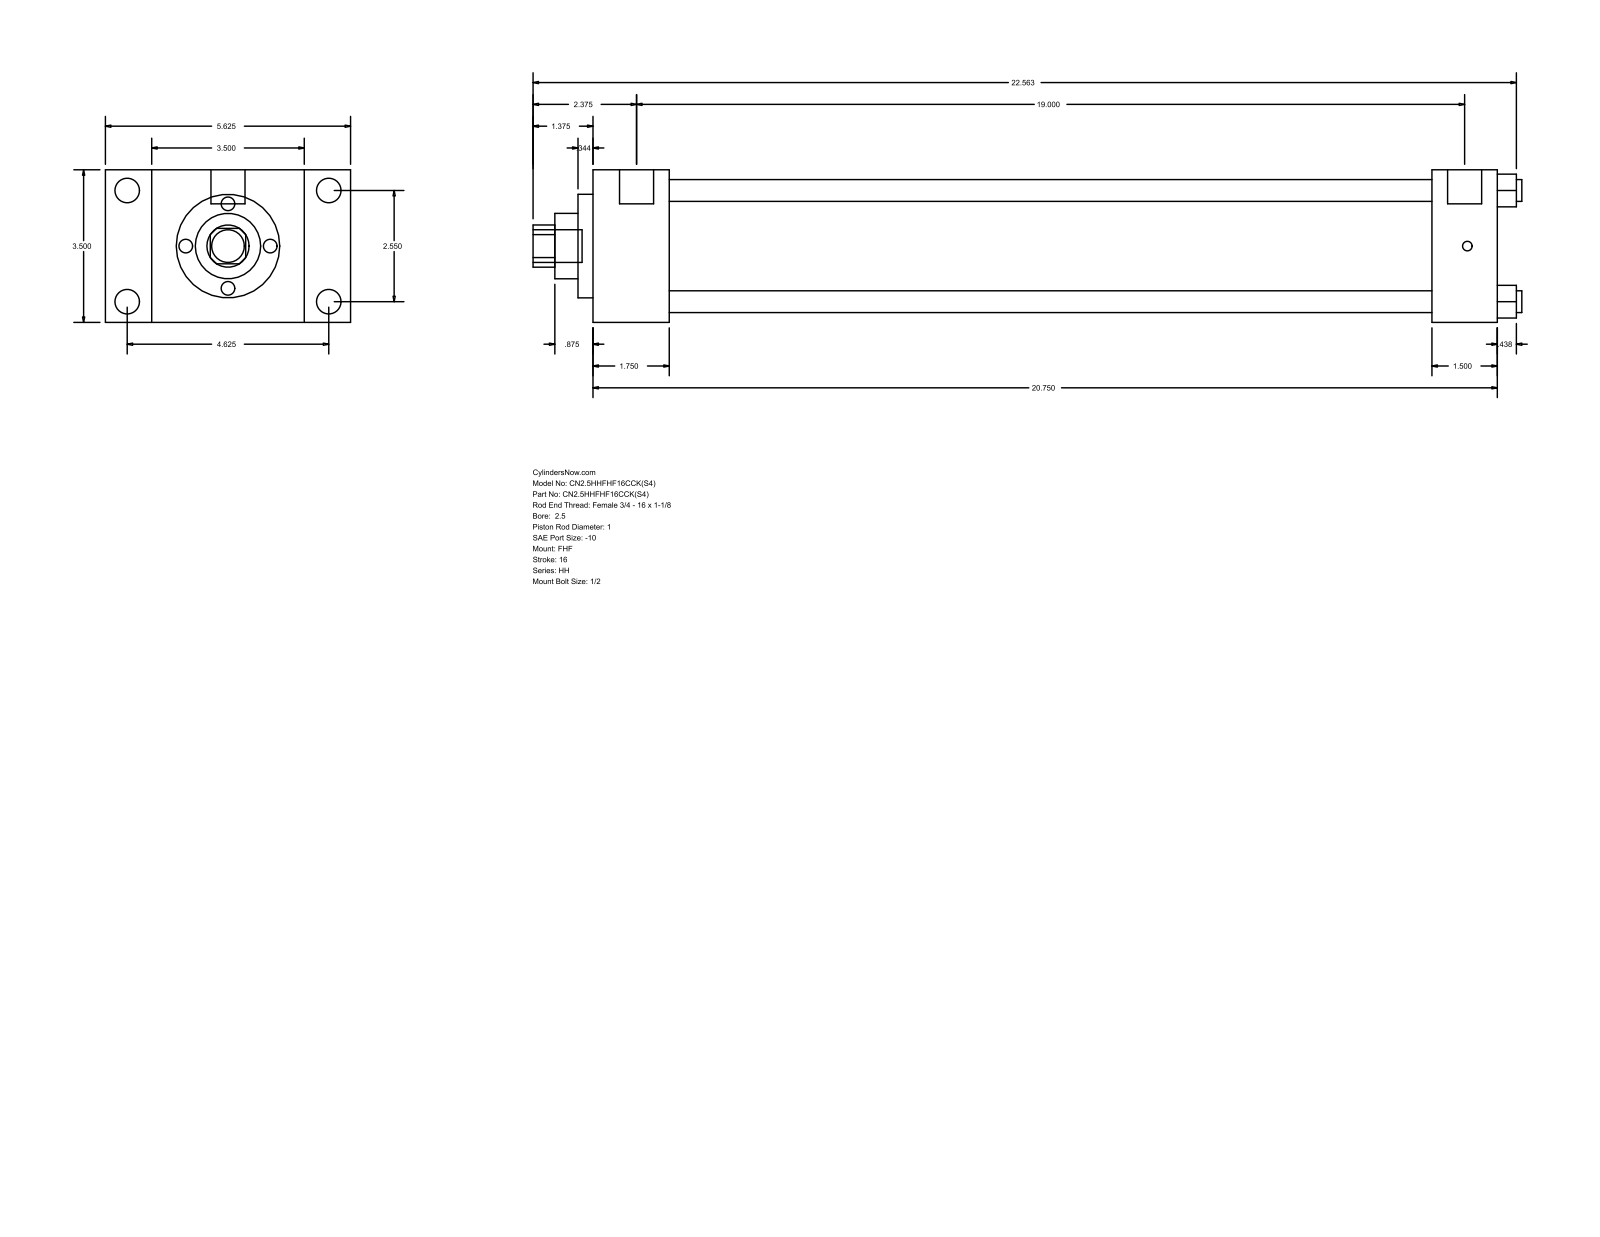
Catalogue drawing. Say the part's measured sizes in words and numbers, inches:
The part is named "HH_FHF__0250_1". Its 3-D file was written by "GSSL Pune (CONFIG_CONTROL_DESIGN)". It is 0 solids with 90 faces: 61 planar, 29 cylindrical and 0 other. Overall it measures 22.687 by 5.625 by 3.5 inches. Round holes: 4 of diameter 0.5, 1 of diameter 1, 1 of diameter 1.5, 1 of diameter 2.375, 1 of diameter 2.875. Round bosses or shafts: 4 of diameter 0.563, 4 of diameter 0.219, 2 of diameter 0.781, 1 of diameter 0.75. Partial cylindrical surfaces (rounded edges, fillets, slot ends): 1 of radius 0.484. The main face-to-face distances are 3.5, 1.75, 1.063, 4.563, 20.75, 19, 5.625, 19.25, 17.5, 1.5. The hole center spacings are 1.803, 2.55, 3.606.
